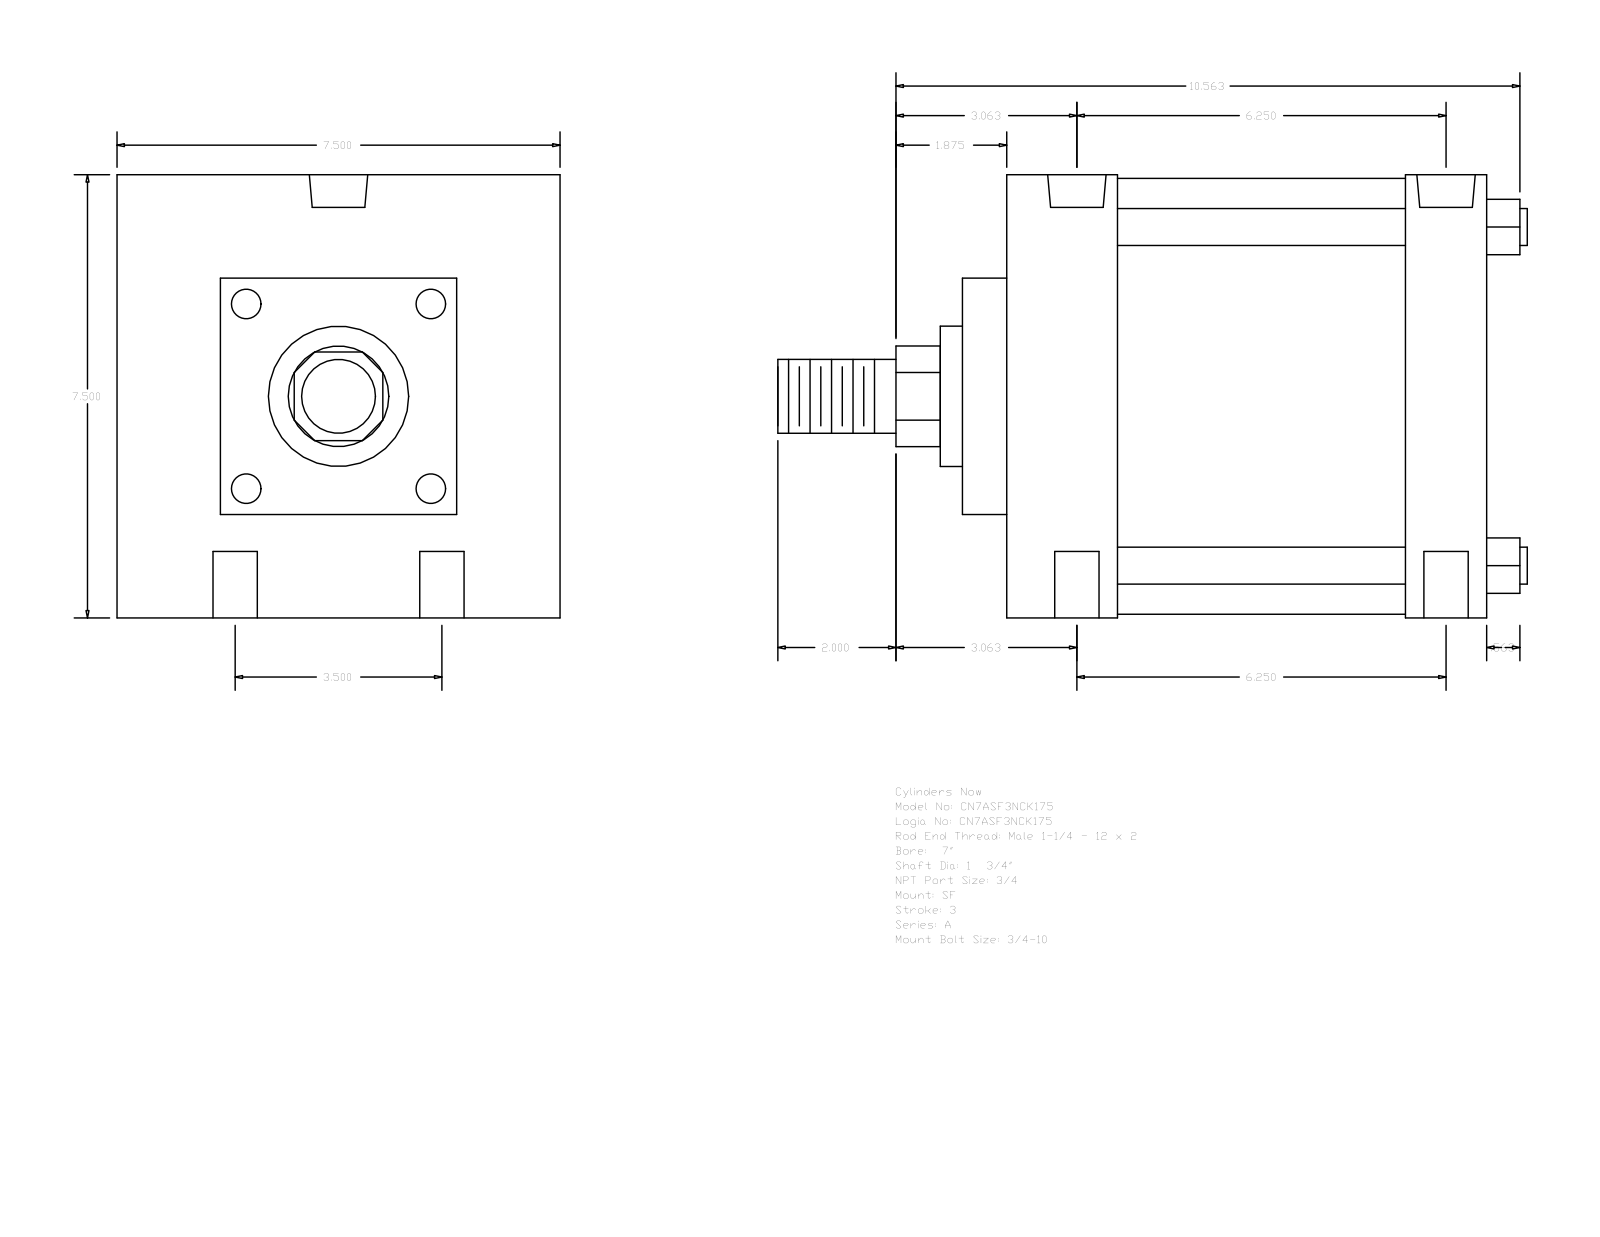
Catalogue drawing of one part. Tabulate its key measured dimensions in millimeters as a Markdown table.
| quantity | value |
| --- | --- |
| part name | A_SF__0700_1.75 |
| STEP written by | GSSL Pune (CONFIG_CONTROL_DESIGN) |
| units | millimeters |
| bodies | 0 solids, 93 faces (67 planar, 26 cylindrical, 0 other) |
| overall size | 322.26 × 190.5 × 190.5 |
| round holes (diameter × count) | 19.05 × 4, 15.08 × 2, 25.12 × 2 |
| round bosses / shafts (diameter × count) | 15.88 × 4, 187.32 × 1, 60.33 × 1, 44.45 × 1, 31.75 × 1 |
| partial cylindrical surfaces (radius × count) | 21.63 × 1 |
| main face-to-face distances | 190.5, 206.38, 146.05, 19.05, 47.63, 171.45, 123.82, 158.75, 34.93, 44.45 |
| hole center spacings | 44.45, 164.86, 158.75, 88.9, 181.95, 147.63 |
